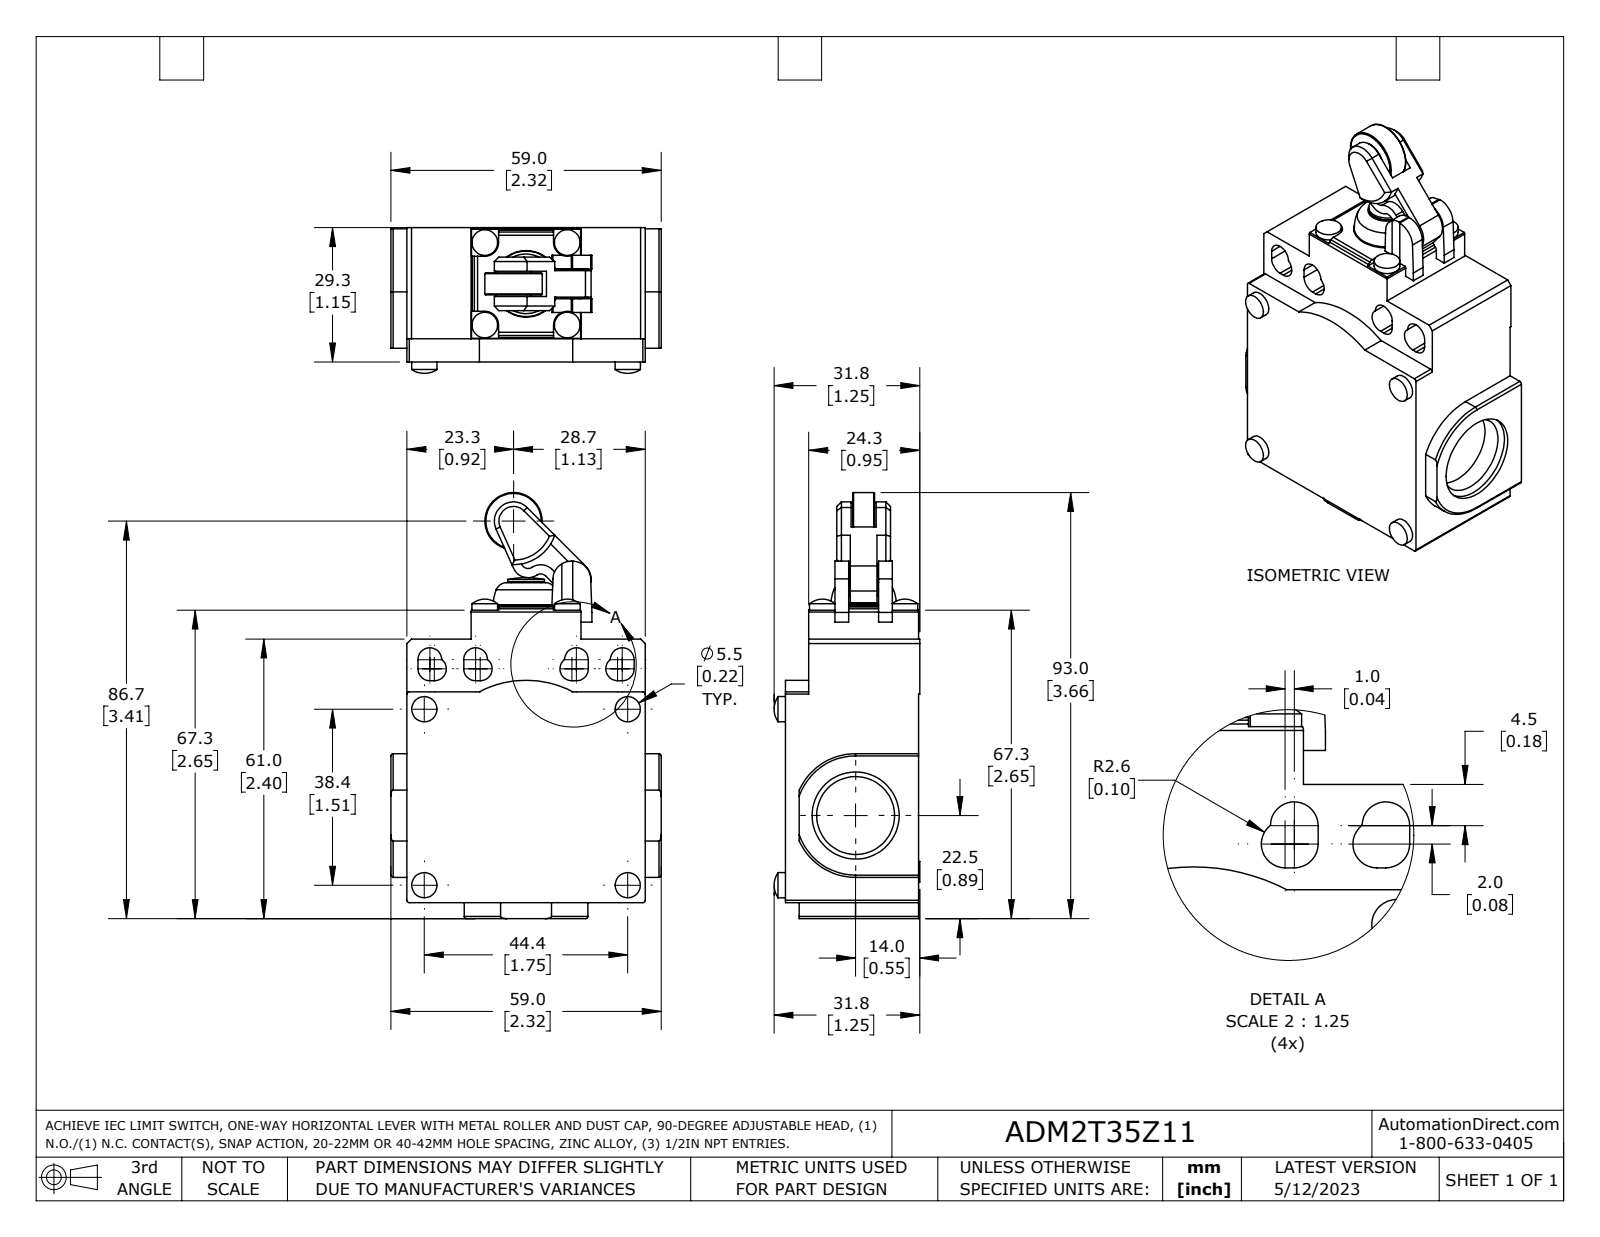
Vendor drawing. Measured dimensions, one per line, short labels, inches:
name: ADM2T35Z11
written by: SolidWorks 2021 (AUTOMOTIVE_DESIGN)
unit: in
bodies: 1 solid, 244 faces (127 planar, 90 cylindrical, 27 other)
size: 3.661 × 2.323 × 1.252
volume: 5.54 in³; area: 29.87 in²
holes: 2× ⌀0.669, 2× ⌀0.748, 1× ⌀0.319, 1× ⌀0.571
bosses: 4× ⌀0.22, 4× ⌀0.217, 1× ⌀0.563, 1× ⌀0.492, 1× ⌀0.315, 1× ⌀0.307, 1× ⌀0.276, 1× ⌀0.256
rounds: 12× R0.102, 10× R0.02, 8× R0.039, 4× R0.118, 2× R0.059, 2× R0.138, 2× R0.157, 2× R0.165
face distances: 1.144, 0.138, 2.047, 0.236, 0.945, 0.098, 1.154, 2.185, 2.264, 1.949
hole spacings: 0.069
